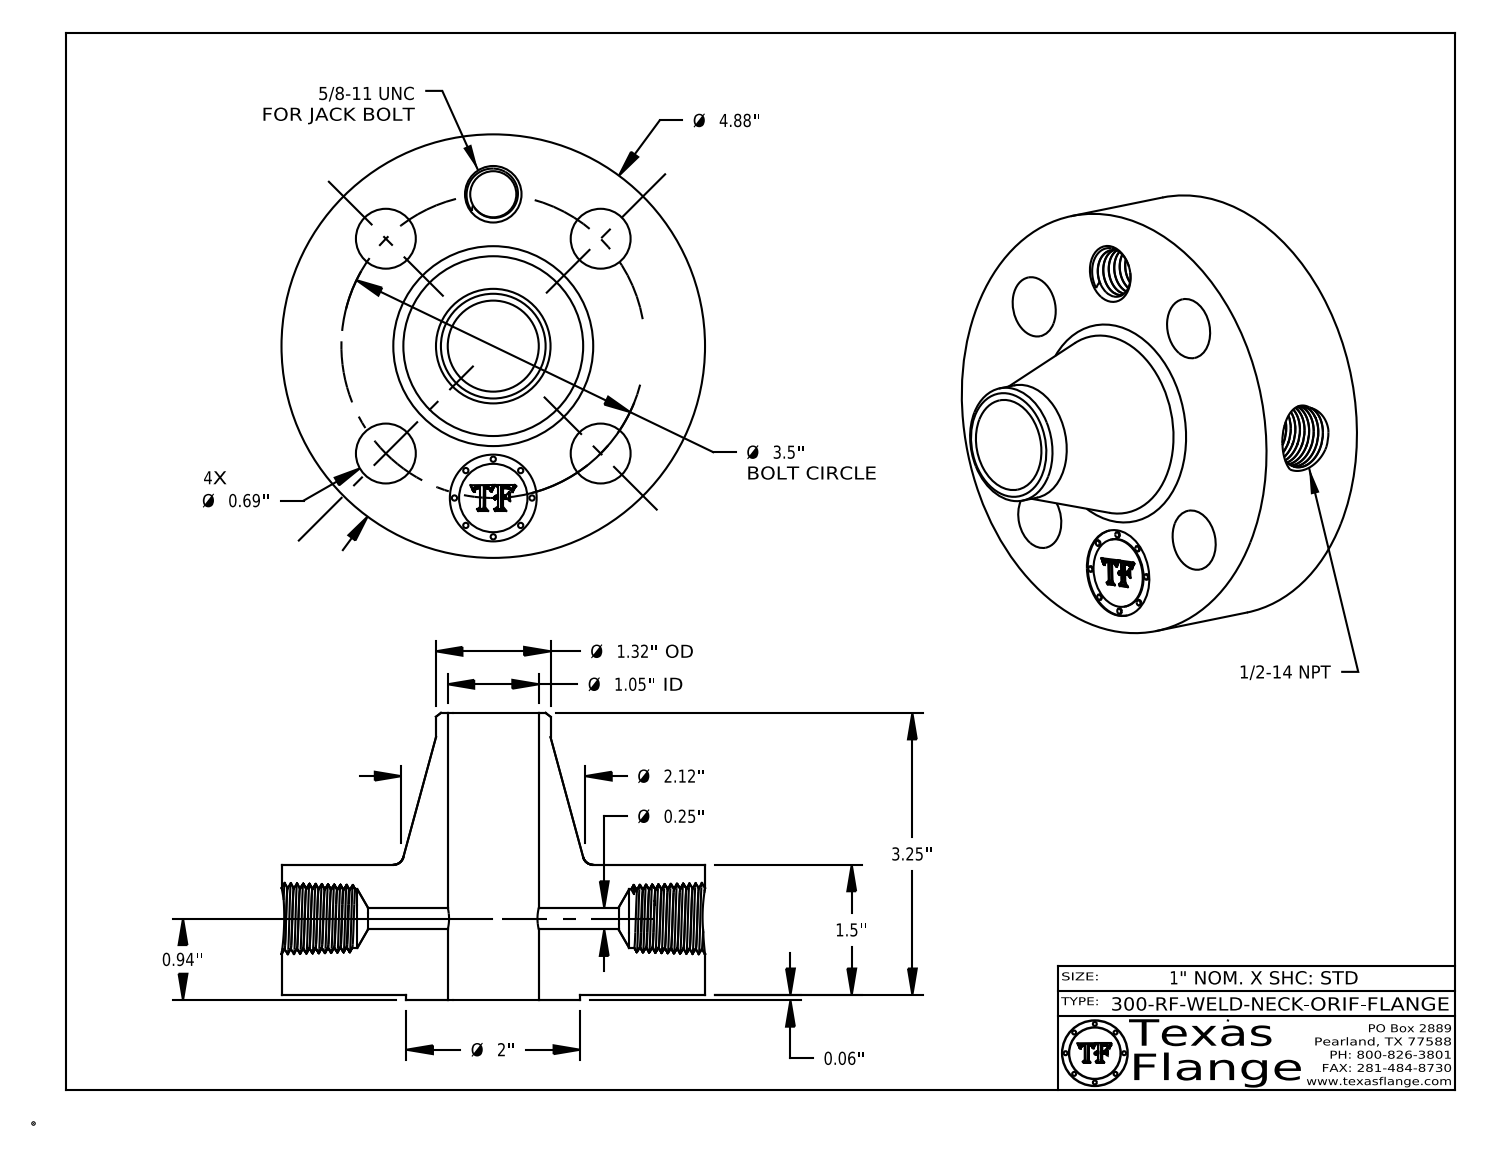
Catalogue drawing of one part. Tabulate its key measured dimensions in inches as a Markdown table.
| quantity | value |
| --- | --- |
| part name | 300-RF-WELD-NECK |
| STEP written by | CATIA V5 STEP AP214 (AUTOMOTIVE_DESIGN) |
| units | inches |
| bodies | 1 solid, 764 faces (369 planar, 87 cylindrical, 308 other) |
| overall size | 4.88 × 4.88 × 3.31 |
| volume | 25.74 in³ |
| surface area | 98.69 in² |
| round holes (diameter × count) | 0.69 × 4, 0.25 × 1, 0.531 × 1, 0.672 × 1, 1 × 1, 1.049 × 1 |
| round bosses / shafts (diameter × count) | 0.061 × 8, 4.88 × 1, 2 × 1, 1.32 × 1, 0.788 × 1 |
| main face-to-face distances | 1.5, 0.06, 1.56, 1.545, 1.485, 0.015, 3.31, 3.25, 1.765, 1.75 |
| hole center spacings | 1.75, 1.339, 2.475, 3.233, 3.5 |
